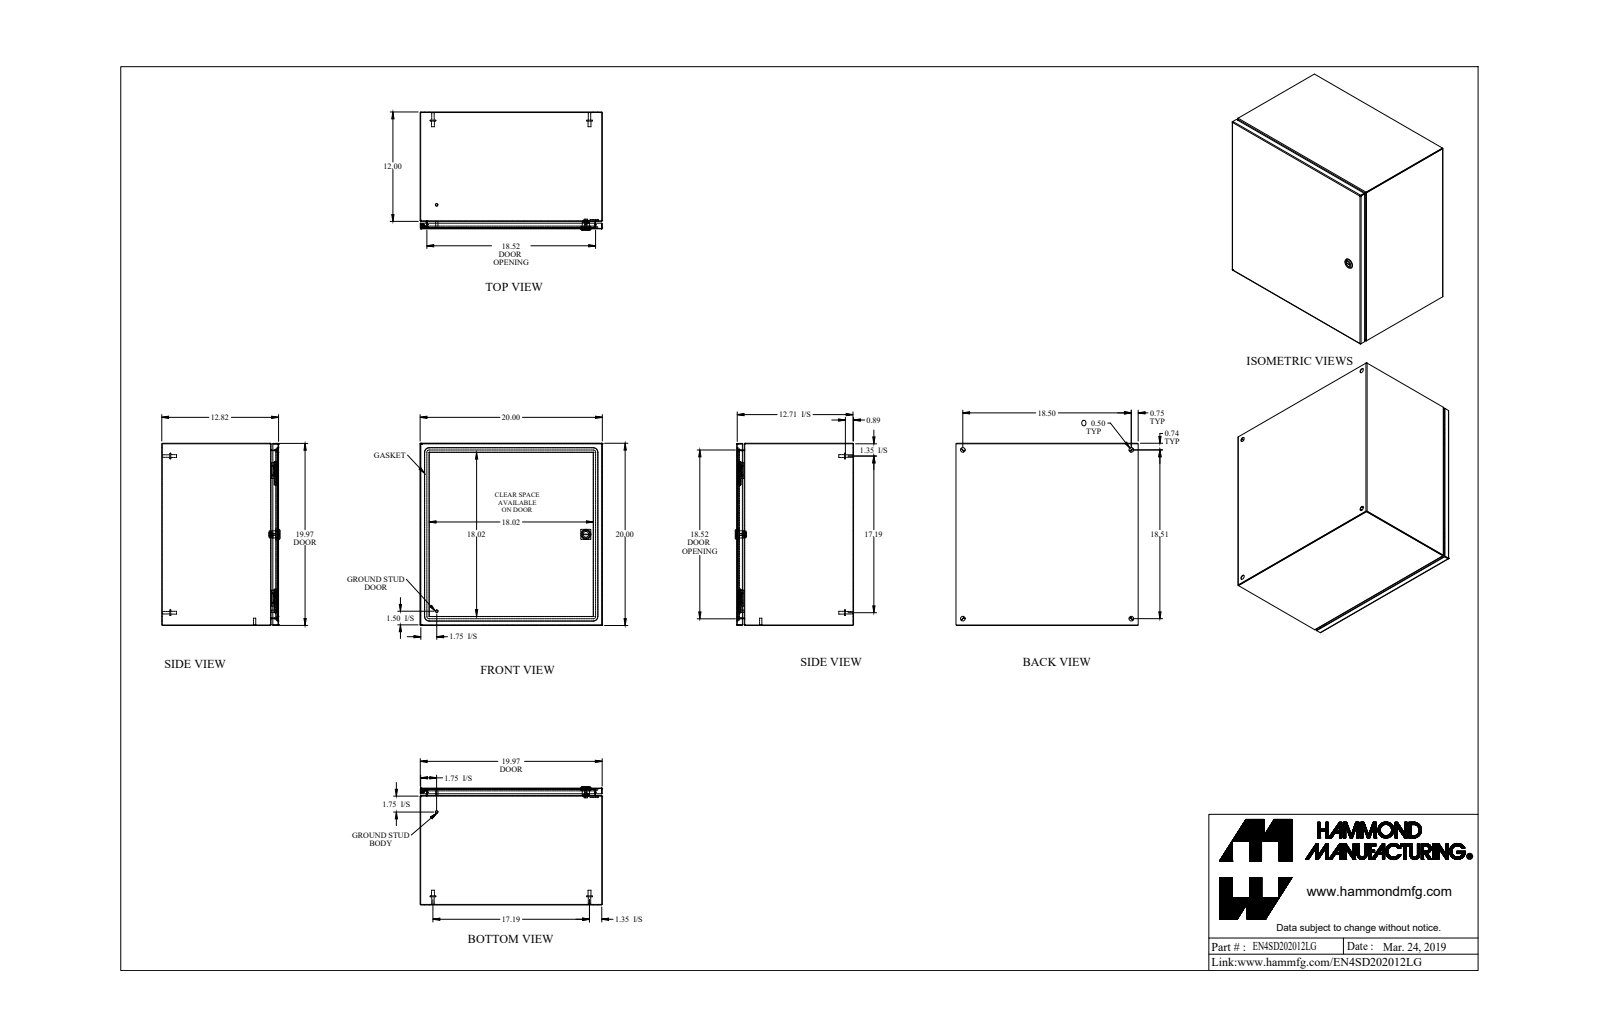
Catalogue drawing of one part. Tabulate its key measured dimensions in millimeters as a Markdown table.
| quantity | value |
| --- | --- |
| part name | EN4SD202012LG_Default |
| STEP written by | SolidWorks 2019 (CONFIG_CONTROL_DESIGN) |
| units | millimeters |
| bodies | 23 solids, 622 faces (293 planar, 201 cylindrical, 128 other) |
| overall size | 508 × 508 × 329.7 |
| volume | 1 916 000 mm³ |
| surface area | 2 586 000 mm² |
| round holes (diameter × count) | 12.7 × 4, 4.4 × 1, 5.9 × 1, 6.1 × 1, 6.1 × 1, 15.9 × 1, 19.9 × 1 |
| round bosses / shafts (diameter × count) | 15.9 × 4, 8 × 4, 6.9 × 4, 7.1 × 2, 6.4 × 2, 27.9 × 1, 13.3 × 1, 11.6 × 1 |
| partial cylindrical surfaces (radius × count) | 0.7 × 19, 2.2 × 19, 4.8 × 12, 0.2 × 4, 1.6 × 4, 6.4 × 4, 12.7 × 4, 3.2 × 2 |
| main face-to-face distances | 1.4, 506.6, 324.2, 505.1, 508, 322.8, 325.7, 20.9, 303.4, 19.4 |
| hole center spacings | 469.9, 470.3, 664.8, 236.4, 236.9, 501.5, 501.7 |
